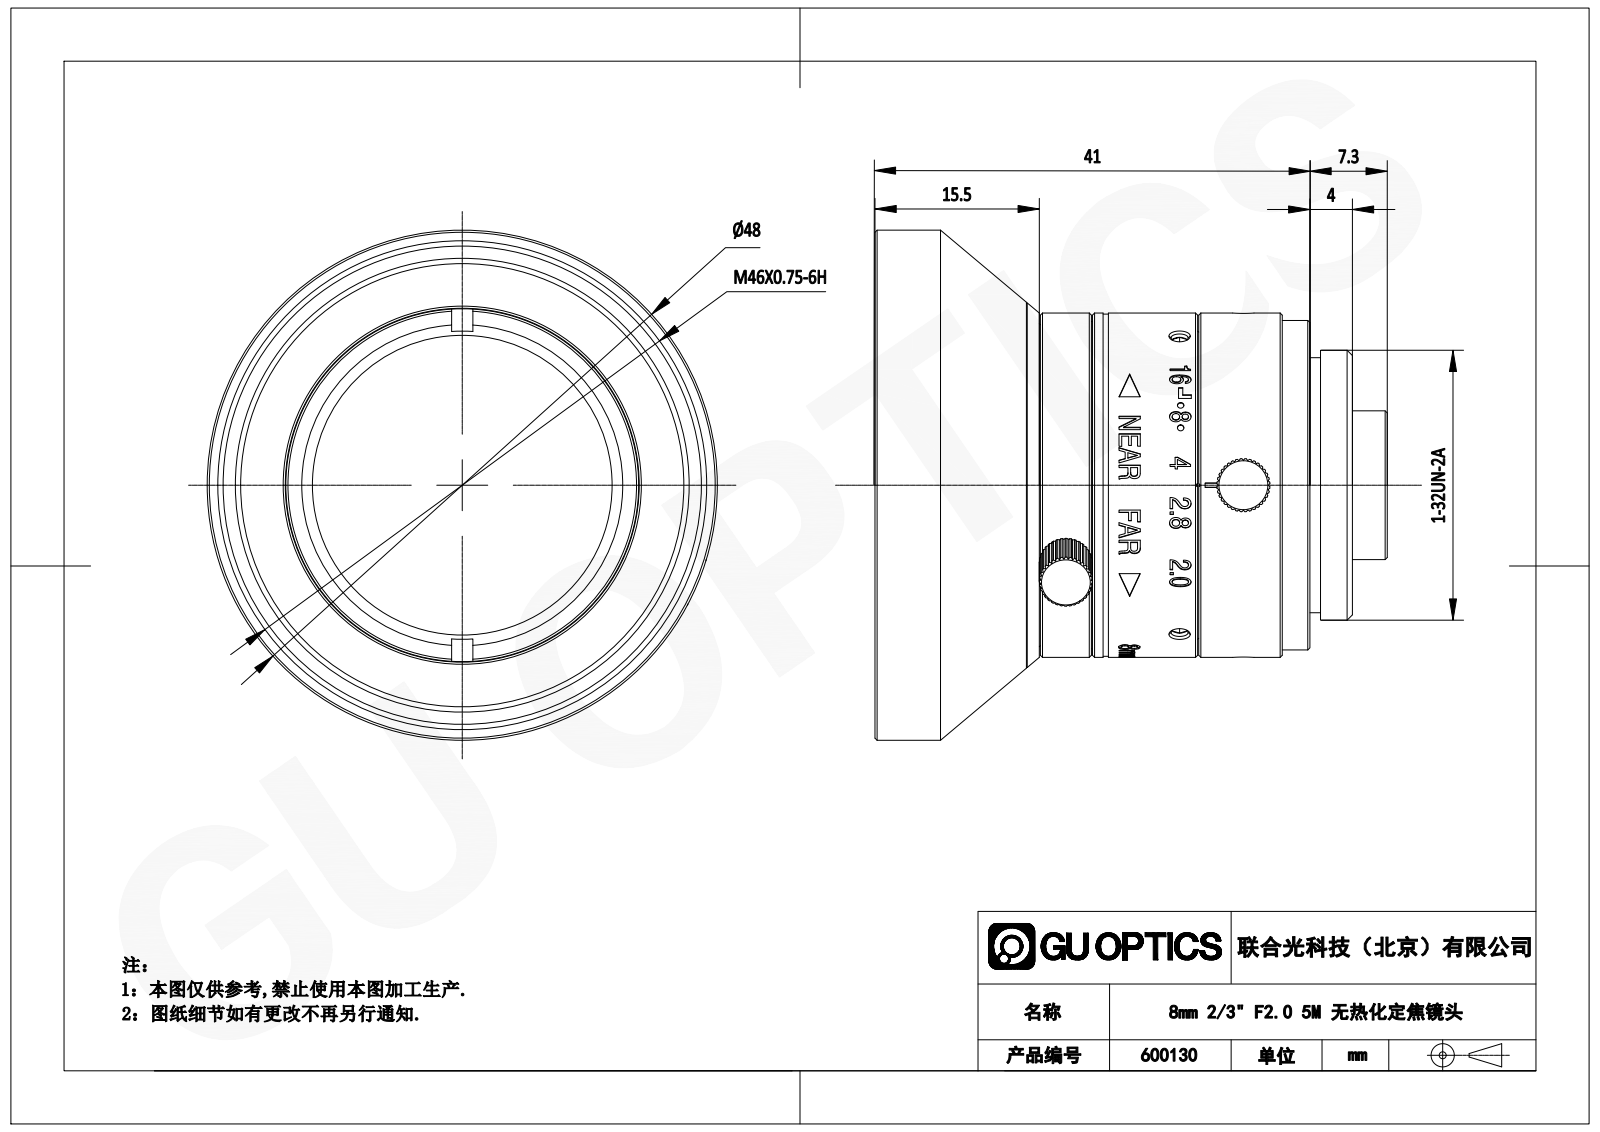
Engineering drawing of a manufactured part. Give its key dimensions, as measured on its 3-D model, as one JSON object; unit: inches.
{"part_name": "600130", "step_written_by": "SolidWorks 2020 (CONFIG_CONTROL_DESIGN)", "units": "inches", "bodies": {"solids": 0, "faces": 2031, "planar": 695, "cylindrical": 449, "other": 887}, "overall_size": [1.943, 1.89, 1.89], "round_holes": [[0.063, 9], [0.043, 6], [0.059, 6], [0.098, 3], [0.106, 3], [0.039, 2], [0.079, 1], [0.26, 1], [0.315, 1], [0.37, 1], [0.409, 1], [0.457, 1]], "round_bosses_or_shafts": [[0.055, 4], [0.098, 3], [0.079, 2], [1.89, 1], [1.291, 1], [1.276, 1], [1.268, 1], [1.213, 1]], "partial_cylinders_radius": [[0.049, 12], [0.039, 5], [0.059, 2], [0.098, 2], [0.633, 1], [0.634, 1], [0.635, 1], [0.635, 1]], "face_to_face_distances": [0.157, 1.29, 0.364, 0.573, 0.922, 1.148, 1.337, 0.772, 0.146, 1.483], "hole_center_spacings": [0.205, 0.386, 0.669, 0.22, 0.252, 0.339, 0.436, 0.472]}
